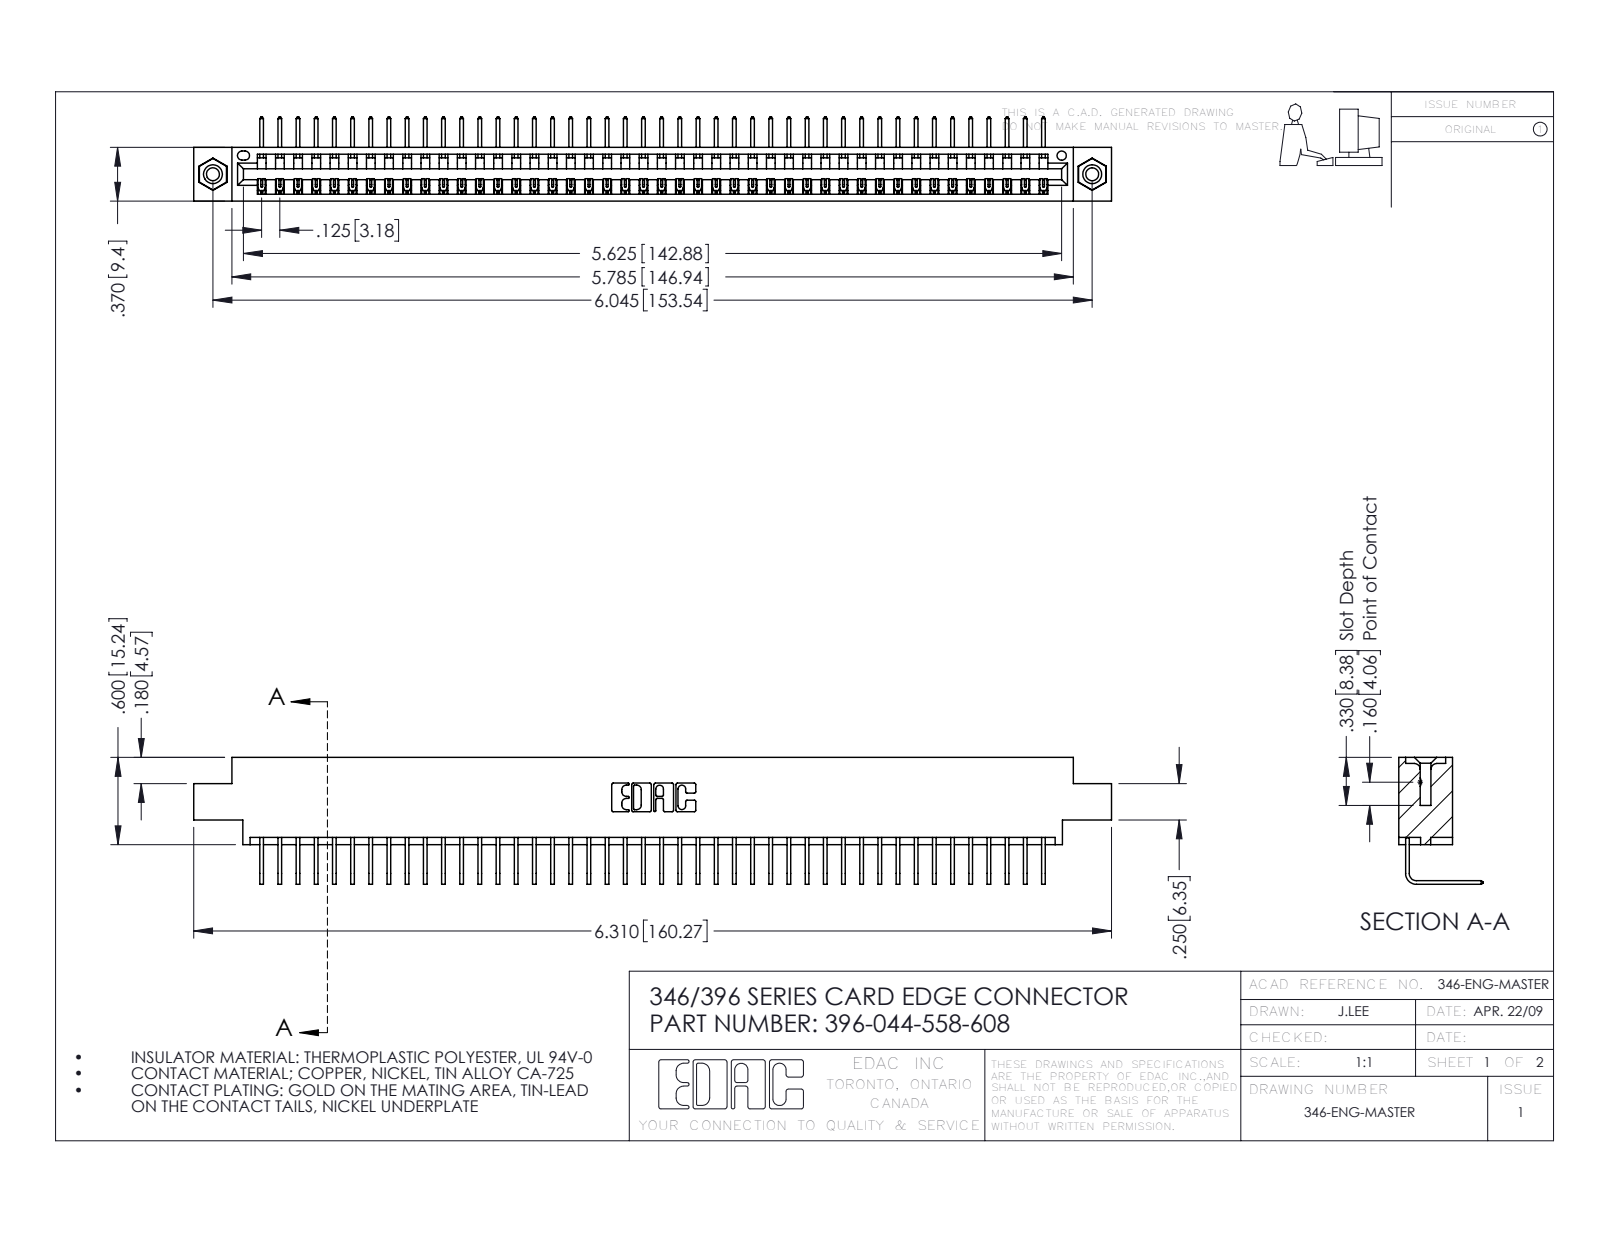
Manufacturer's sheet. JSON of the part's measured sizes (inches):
{"part_name": "345-250-001_345-250-003-102; 346 Part_0.170 Offset - 0.156 Dia-TI; 396-044-558-608; 345-292-001_558 Tail - 2", "step_written_by": "SolidWorks 2016 (CONFIG_CONTROL_DESIGN)", "units": "inches", "bodies": {"solids": 47, "faces": 2826, "planar": 1960, "cylindrical": 850, "other": 16}, "overall_size": [6.31, 0.873, 0.58], "volume_in3": 0.936, "surface_area_in2": 31.39, "round_holes": [[0.089, 2], [0.125, 2], [0.156, 2], [0.064, 1]], "round_bosses_or_shafts": [[0.155, 2]], "partial_cylinders_radius": [[0.006, 88], [0.01, 22], [0.007, 6], [0.031, 6], [0.026, 3], [0.031, 2], [0.04, 2], [0.014, 1]], "face_to_face_distances": [0.322, 0.048, 0.37, 0.25, 0.298, 0.025, 0.072, 0.222, 0.148, 0.1], "hole_center_spacings": [0.246, 5.836, 6.045]}
